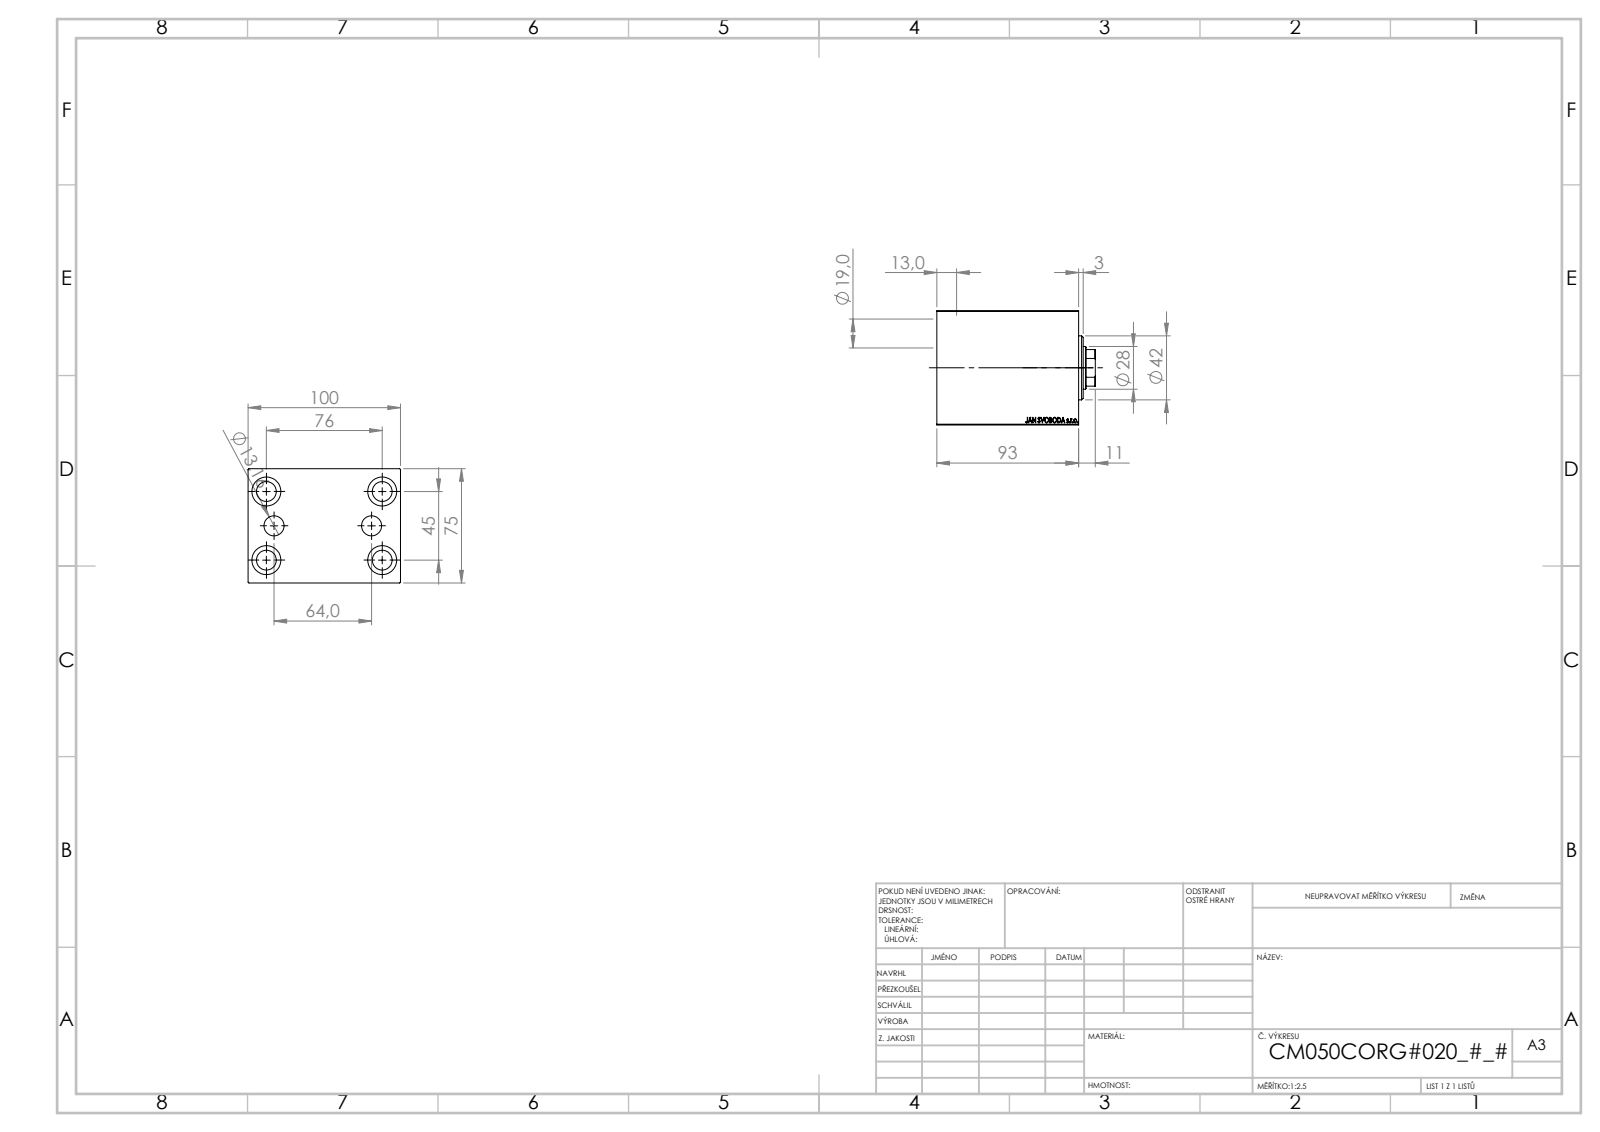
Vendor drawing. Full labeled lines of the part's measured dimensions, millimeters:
Part name (STEP PRODUCT): V450CM_VC_B; V450CM_C_Body; V450CM_C_VCP
STEP written by: SolidWorks 2019 (CONFIG_CONTROL_DESIGN)
Units: millimetres
Bodies: 3 solids, 855 faces (407 planar, 54 cylindrical, 394 other)
Overall size (bounding box): 104 × 100 × 75
Volume: 617 063 mm³ · Surface area: 94 754 mm²
Round holes (diameter × count): ⌀13 ×4, ⌀19 ×4, ⌀13.16 ×2, ⌀18.5 ×1, ⌀28 ×1, ⌀31.5 ×1, ⌀50 ×1, ⌀52 ×1, ⌀57 ×1
Round bosses / shafts (diameter × count): ⌀42 ×1
Partial cylindrical surfaces — rounded edges, fillets, slot ends (radius × count): R13.5 ×1
Main face-to-face distances: 75, 100, 93, 51, 42, 10, 21.6, 29.4, 71.4, 61.4
Hole centre spacings: 44.16, 23.05, 23.56, 45, 72.58, 74.48, 76, 88.32
